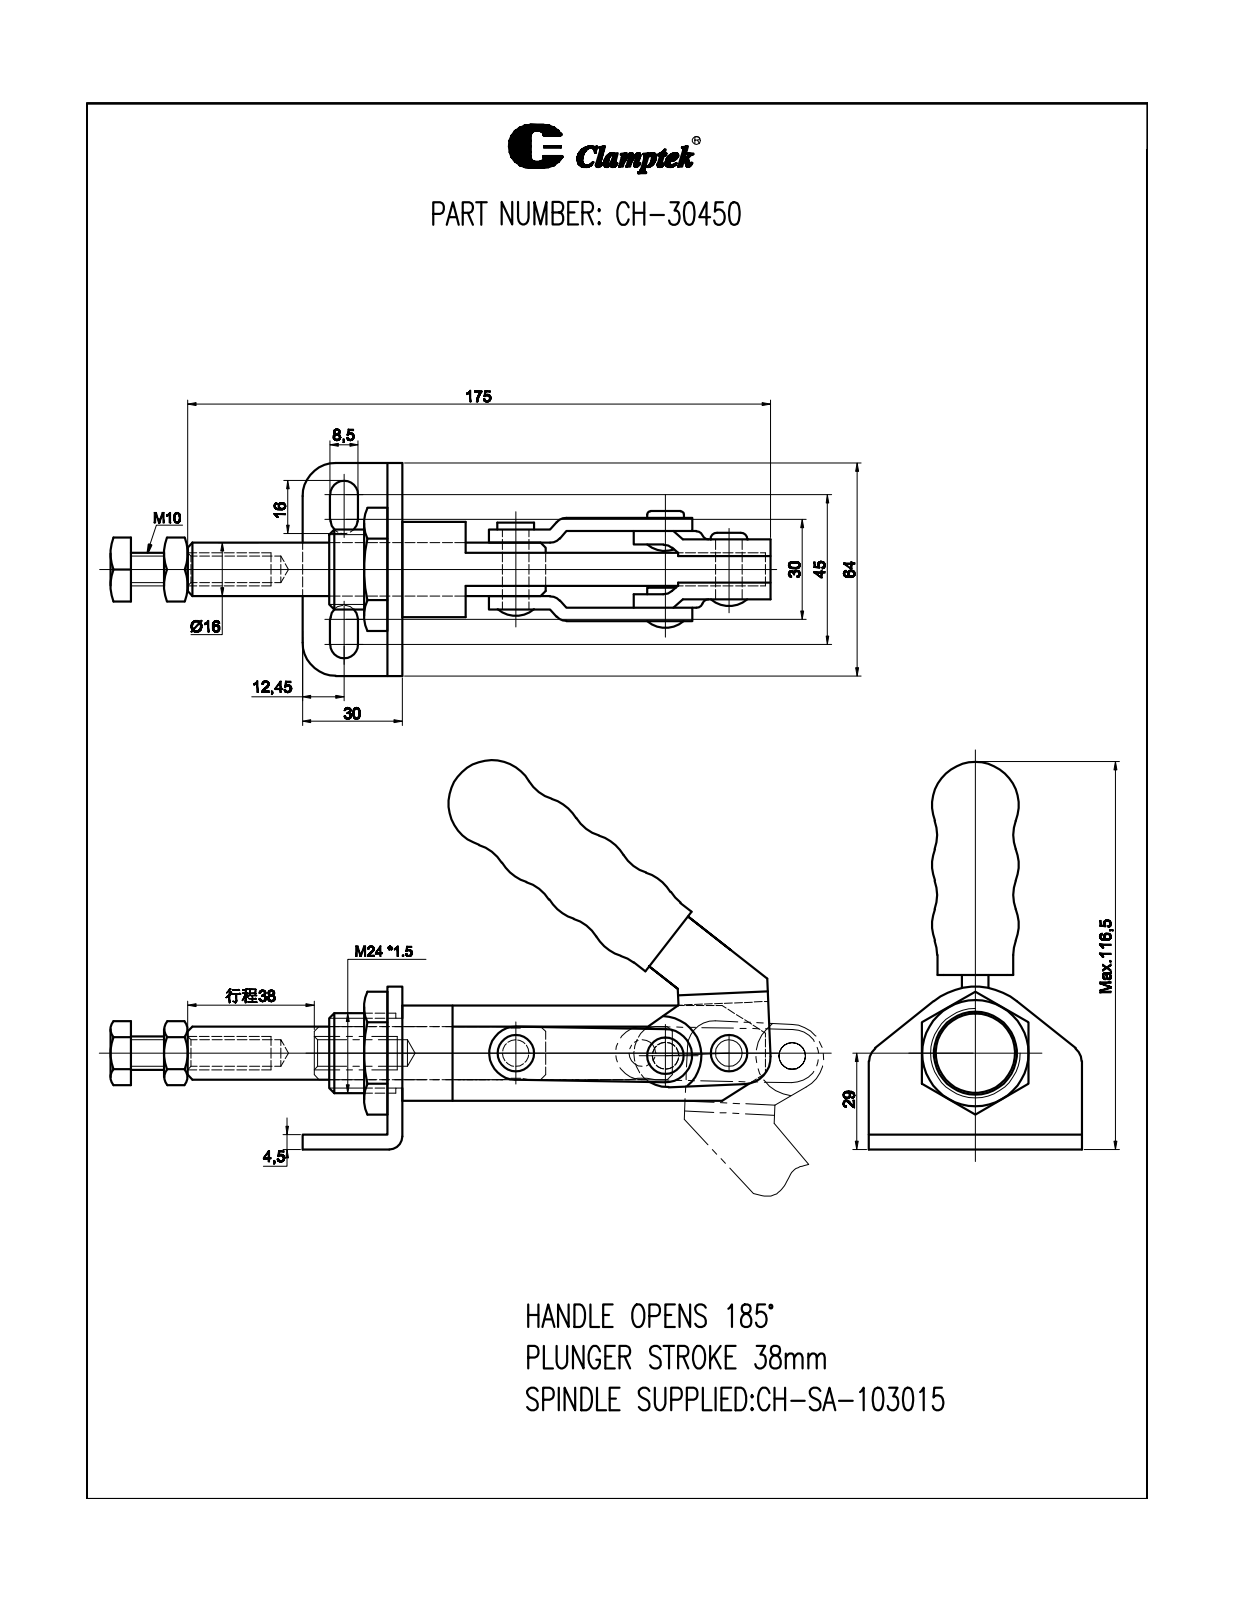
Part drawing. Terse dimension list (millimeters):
name: CH-30450-03_??; CH-30450-06_??; CH-30450-07_??; CH-30450-02_?? (+8 more)
written by: SolidWorks 2005179 (CONFIG_CONTROL_DESIGN)
unit: mm
bodies: 14 solids, 526 faces (168 planar, 215 cylindrical, 143 other)
size: 197.5 × 118.4 × 64
volume: 109 789 mm³; area: 63 365 mm²
holes: 3× ⌀8, 2× ⌀5.59, 1× ⌀7.2, 1× ⌀8.5, 1× ⌀10.5, 1× ⌀16, 1× ⌀22.5, 1× ⌀25
bosses: 3× ⌀11, 1× ⌀28.6, 1× ⌀24, 1× ⌀20, 1× ⌀12.7, 1× ⌀7.9
rounds: 8× R1, 8× R4, 4× R4.25, 3× R8, 3× R10, 2× R5, 1× R4.5, 1× R9
face distances: 1, 10, 2, 8, 9, 4.5, 4, 11, 6.5, 16.5
hole spacings: 19, 45, 64
